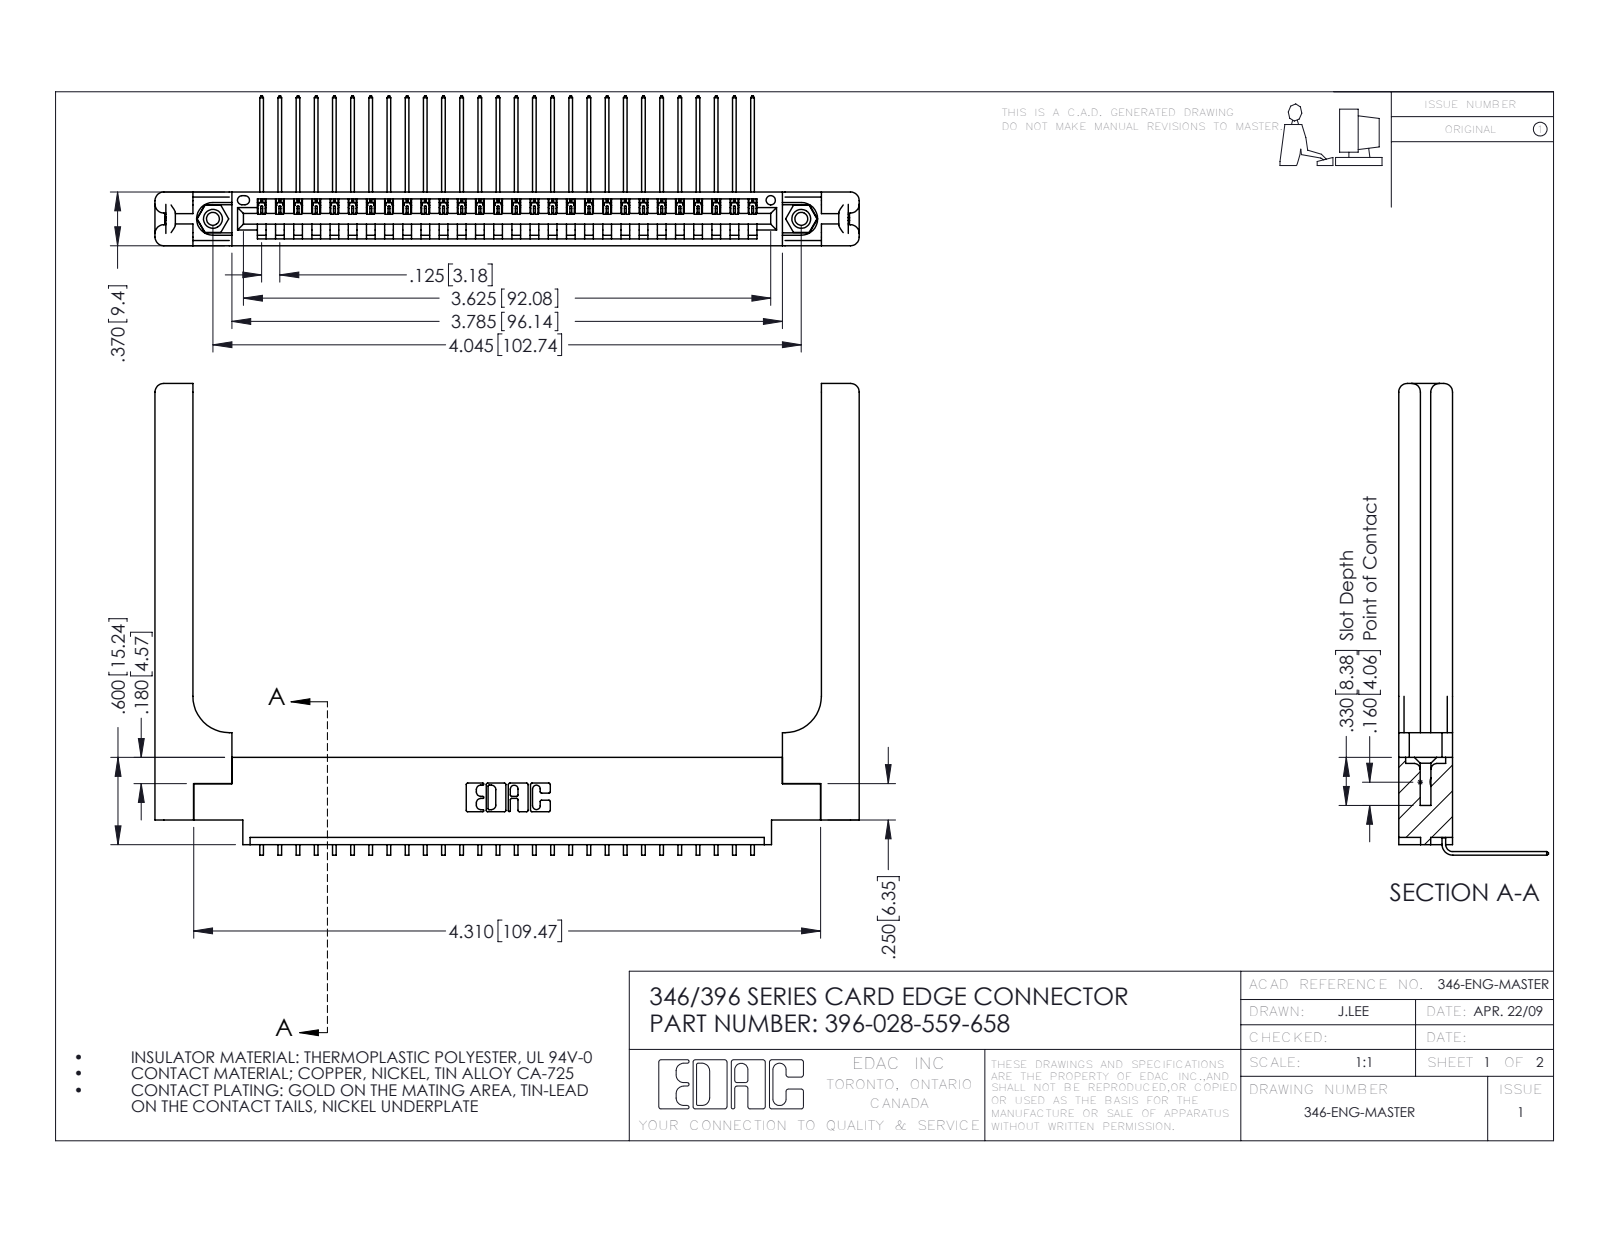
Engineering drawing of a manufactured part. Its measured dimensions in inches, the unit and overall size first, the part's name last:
Units: inches
Overall size (bounding box): 4.841 × 3.243 × 1.03
Round holes (diameter × count): ⌀0.089 ×2, ⌀0.125 ×2, ⌀0.156 ×2, ⌀0.064 ×1
Round bosses / shafts (diameter × count): ⌀0.155 ×2
Partial cylindrical surfaces — rounded edges, fillets, slot ends (radius × count): R0.006 ×56, R0.01 ×22, R0.06 ×16, R0.007 ×6, R0.031 ×6, R0.026 ×3, R0.03 ×2, R0.031 ×2
Main face-to-face distances: 0.37, 0.072, 0.048, 0.322, 0.148, 0.15, 0.025, 0.25, 0.298, 0.076
Hole centre spacings: 0.246, 3.837, 4.045
Volume: 1.167 in³ · Surface area: 31.39 in²
Bodies: 33 solids, 2062 faces (1404 planar, 598 cylindrical, 60 other)
Part name (STEP PRODUCT): 346 Part_0.170 Offset - 0.156 Dia-TH; 346-220-058_345-220-058; 396-028-559-658; 345-250-001_345-250-001-102 (+1 more)
STEP written by: SolidWorks 2016 (CONFIG_CONTROL_DESIGN)
